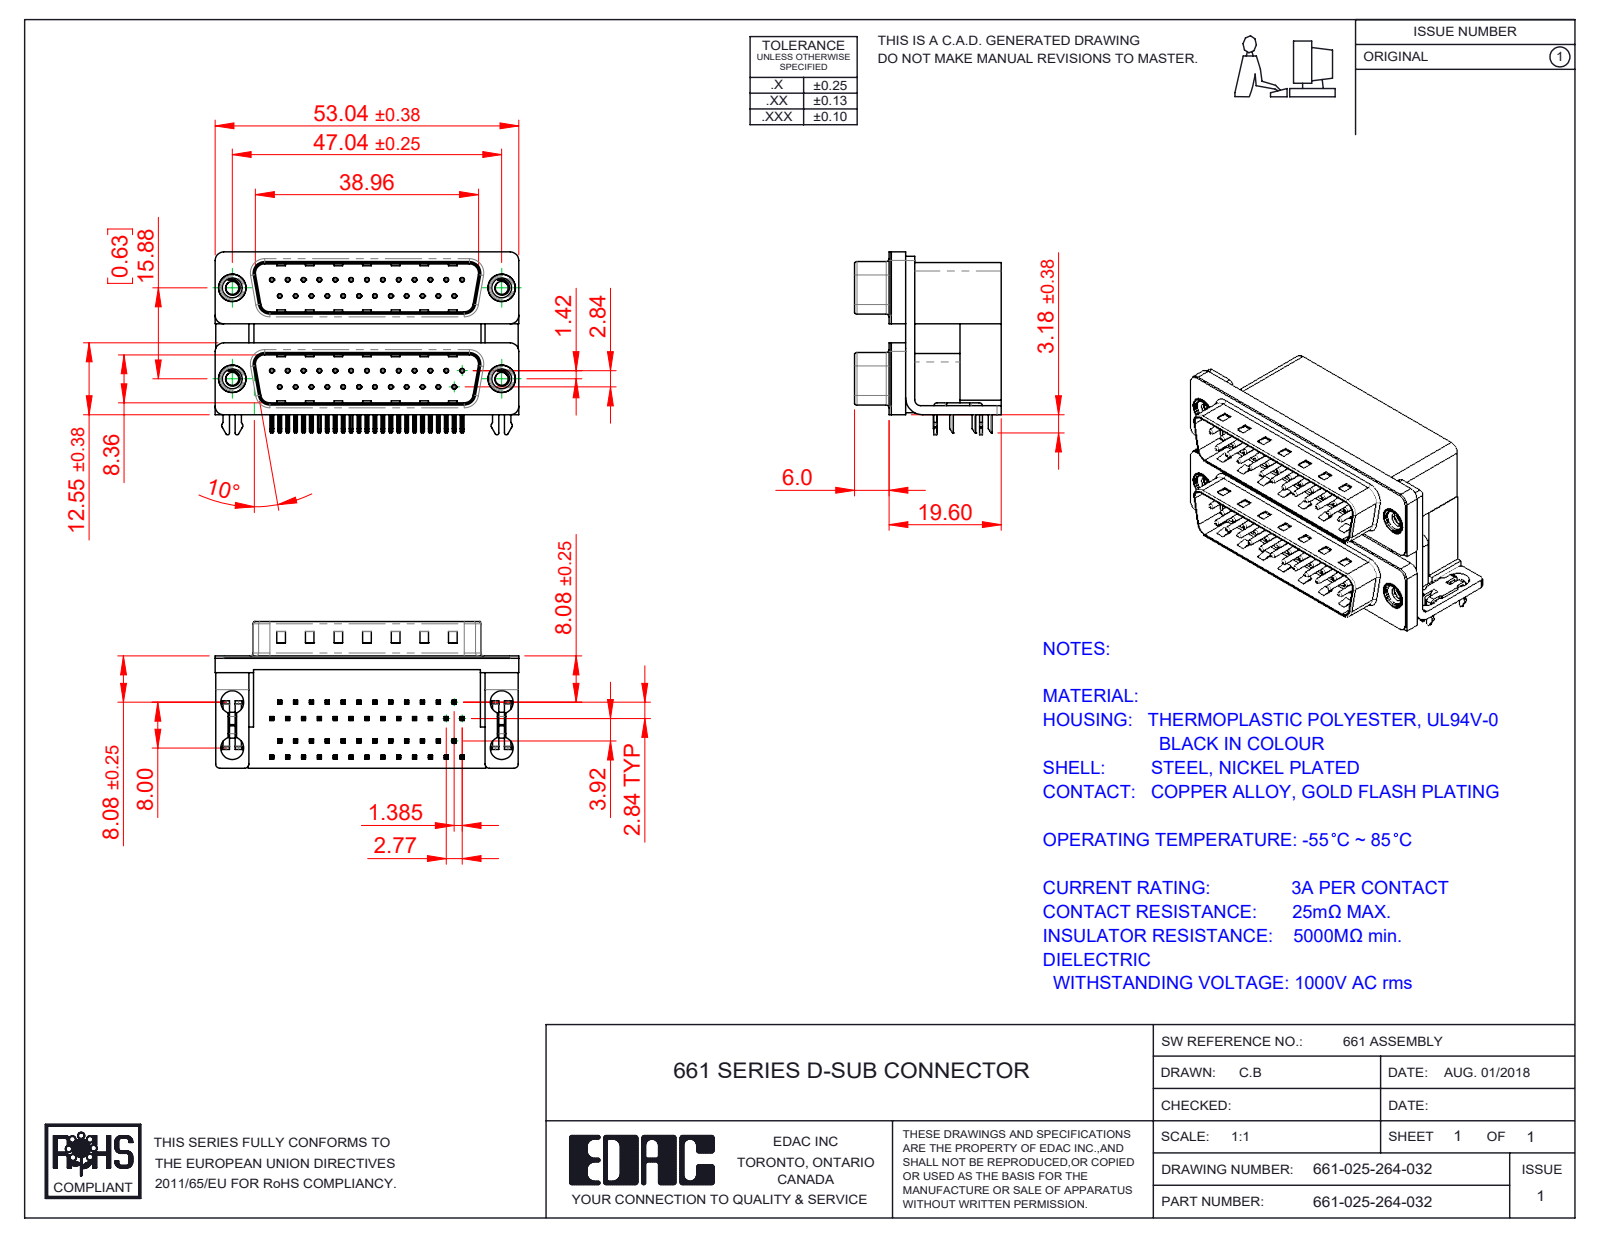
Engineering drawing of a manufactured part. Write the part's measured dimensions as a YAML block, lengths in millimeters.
part_name: "661 Mounting Bracket_2ProngL; 661 2 Prong Board Lock_3; 661 Threaded Rivet_4-40; 661 Contact Top Lower (+8 more)"
step_written_by: "SolidWorks 2020 (CONFIG_CONTROL_DESIGN)"
units: millimeters
bodies: {solids: 63, faces: 4766, planar: 3040, cylindrical: 1332, other: 394}
overall_size: [53.04, 31.93, 25.6]
volume: 20280
surface_area: 21486
round_holes:
  - {diameter: 0.35, count: 50}
  - {diameter: 0.8, count: 50}
  - {diameter: 4, count: 8}
  - {diameter: 2.26, count: 4}
  - {diameter: 3.5, count: 4}
  - {diameter: 4.8, count: 4}
  - {diameter: 5, count: 4}
round_bosses_or_shafts:
  - {diameter: 0.75, count: 50}
  - {diameter: 4.9, count: 4}
  - {diameter: 4.75, count: 4}
  - {diameter: 3.9, count: 4}
partial_cylinders:
  - {radius: 0.25, count: 210}
  - {radius: 0.12, count: 100}
  - {radius: 0.5, count: 20}
  - {radius: 1.5, count: 13}
  - {radius: 0.75, count: 10}
  - {radius: 0.9, count: 8}
  - {radius: 1.6, count: 8}
  - {radius: 2, count: 8}
face_to_face_distances: [0.4, 19.2, 7.2, 12, 10.7, 15.87, 16.7, 9.5, 2.5, 15.53]
hole_center_spacings: [3.16, 2.77, 5.54, 8.31, 11.08, 13.85, 16.62, 5.03]
